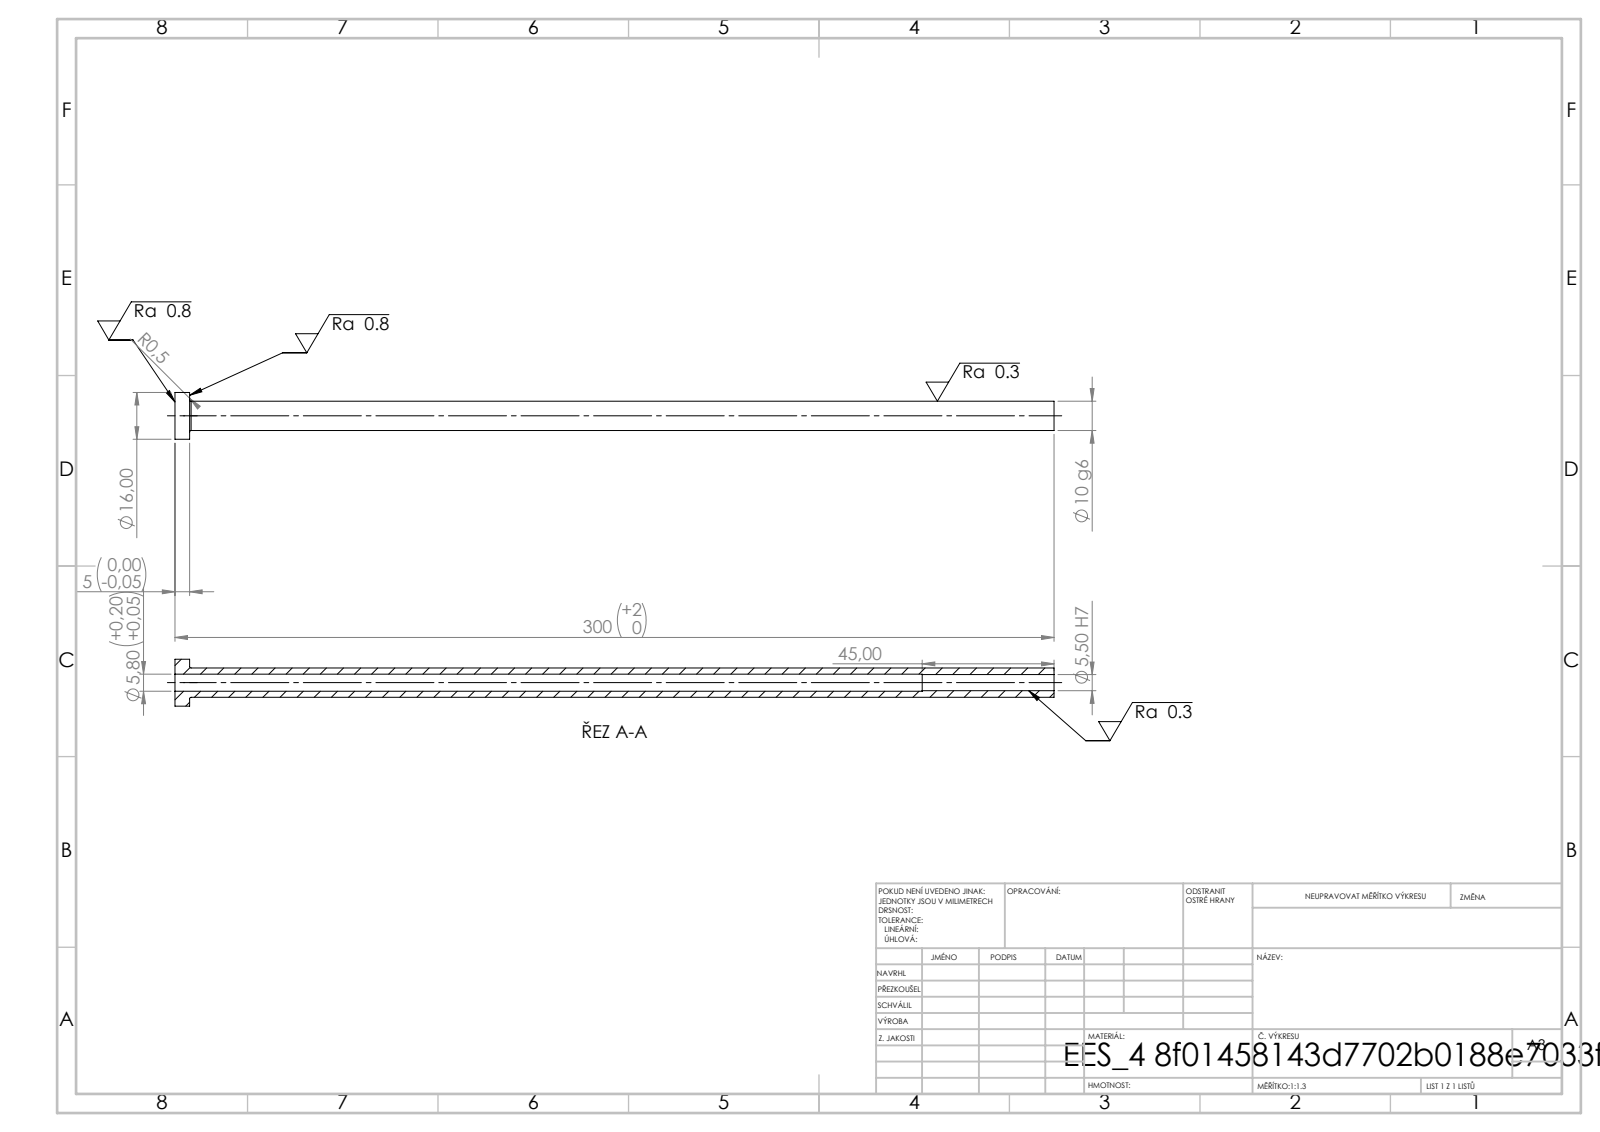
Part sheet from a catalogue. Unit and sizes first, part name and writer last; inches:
Units: inches
Overall size (bounding box): 11.811 × 0.63 × 0.63
Round holes (diameter × count): ⌀0.217 ×1, ⌀0.228 ×1
Round bosses / shafts (diameter × count): ⌀0.63 ×1, ⌀0.394 ×1
Main face-to-face distances: 0.197, 11.811, 11.614, 10.039, 9.843, 1.772
Volume: 0.999 in³ · Surface area: 23.7 in²
Bodies: 1 solid, 14 faces (4 planar, 8 cylindrical, 2 other)
STEP written by: SolidWorks 2019 (CONFIG_CONTROL_DESIGN)
